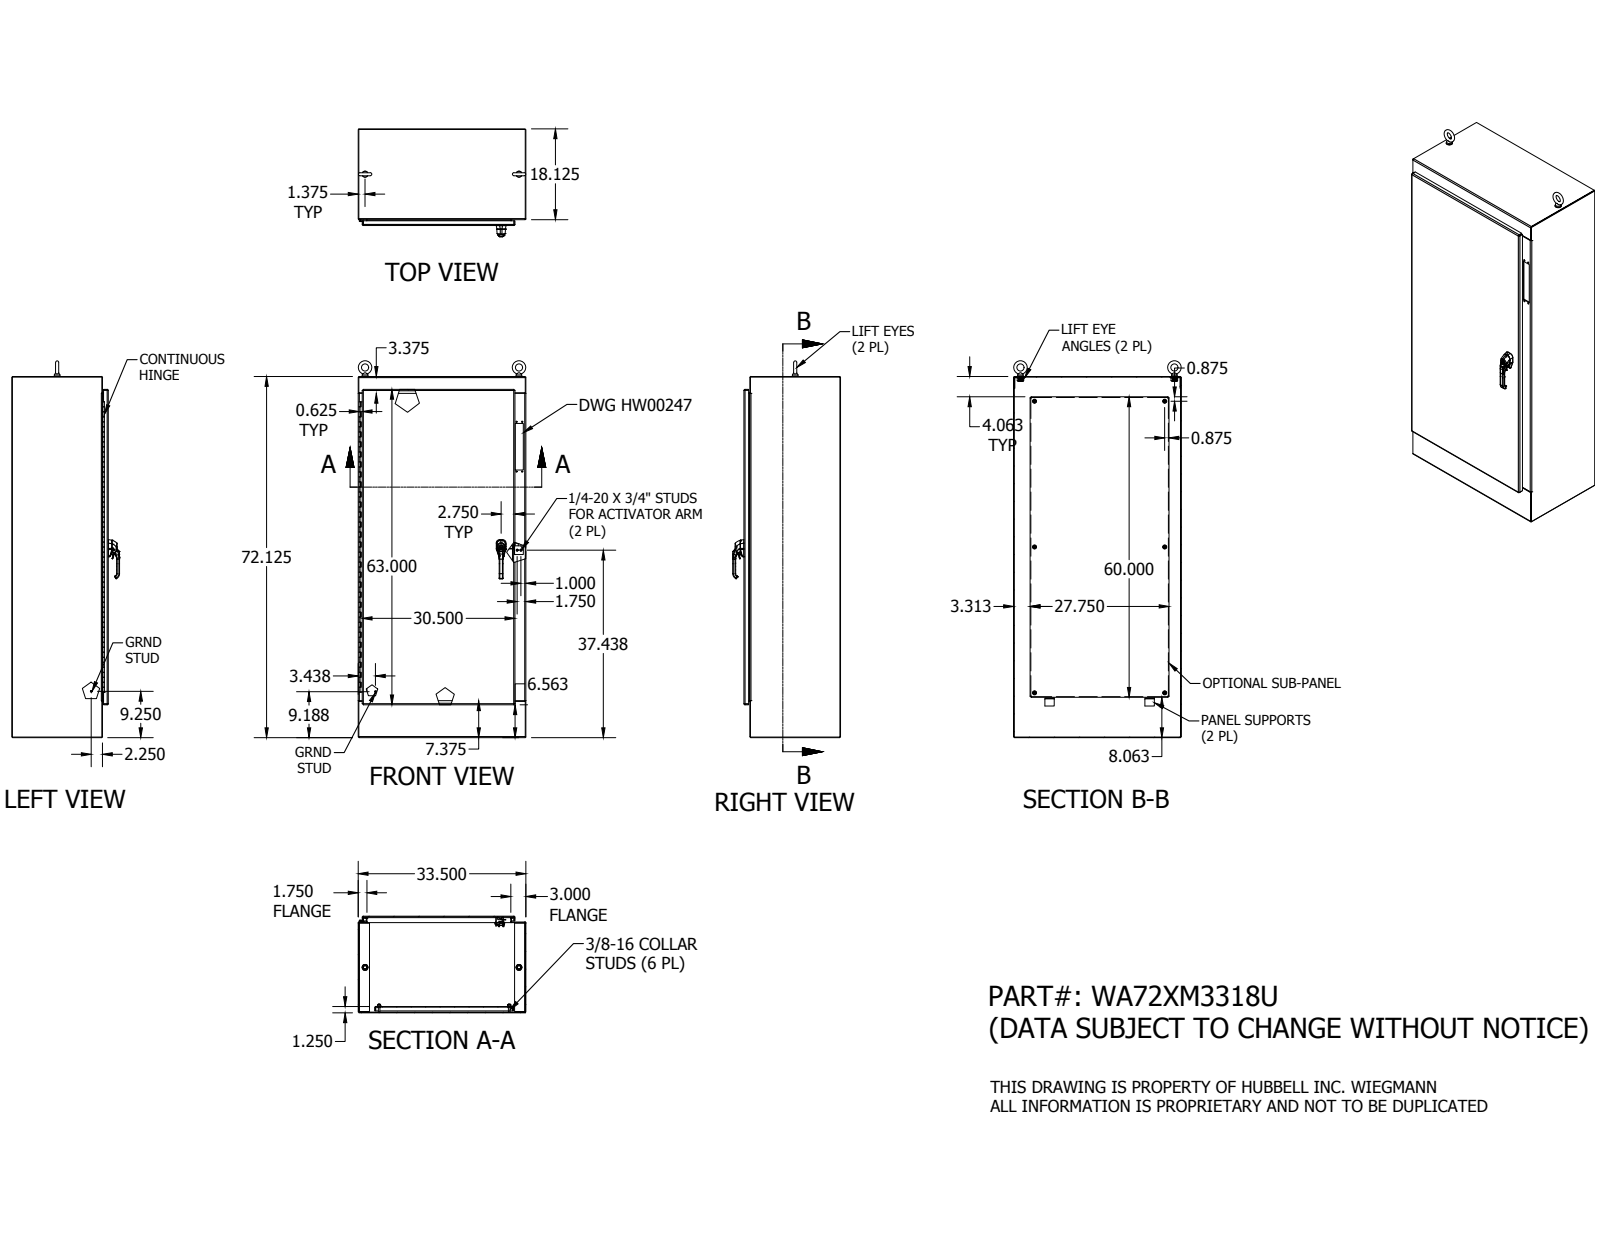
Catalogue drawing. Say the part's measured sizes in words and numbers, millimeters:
The part is named "WA72XM33U_BACK; WA72XM18U_RIGHT_SIDE; WA72XM18U_LEFT_SIDE; WAXM3318U_TOP_ENWDALL (+8 more)". Its 3-D file was written by "Autodesk Inventor 2014 (AUTOMOTIVE_DESIGN)". It is 103 solids with 3698 faces: 1615 planar, 1232 cylindrical and 851 other. Overall it measures 1911.29 by 850.9 by 547.14 millimeters. Its volume is 23 130 000 cubic millimeters and its surface area 14 830 000 square millimeters. Round holes: 10 of diameter 9.52, 8 of diameter 7.02, 7 of diameter 7.14, 6 of diameter 3.96, 6 of diameter 6.35, 6 of diameter 7.8, 6 of diameter 14.29, 4 of diameter 5.08, 4 of diameter 7.37, 3 of diameter 5.4, 2 of diameter 3, 2 of diameter 3.17. Round bosses or shafts: 10 of diameter 15.88, 9 of diameter 8.38, 6 of diameter 14.29, 4 of diameter 9.52, 4 of diameter 8.56, 4 of diameter 6.35, 3 of diameter 6, 2 of diameter 31.75. Partial cylindrical surfaces (rounded edges, fillets, slot ends): 187 of radius 0.5, 109 of radius 0.3, 48 of radius 0.51, 21 of radius 0.47, 21 of radius 2.38, 20 of radius 5.56, 14 of radius 1.27, 14 of radius 2. The main face-to-face distances are 3.17, 3.18, 28.58, 486.84, 483.67, 490.02, 486.85, 31.75, 455.09, 458.27. The hole center spacings are 619.53, 660.4, 9.67, 9.69, 9.72, 19.05, 19.36, 19.4.
